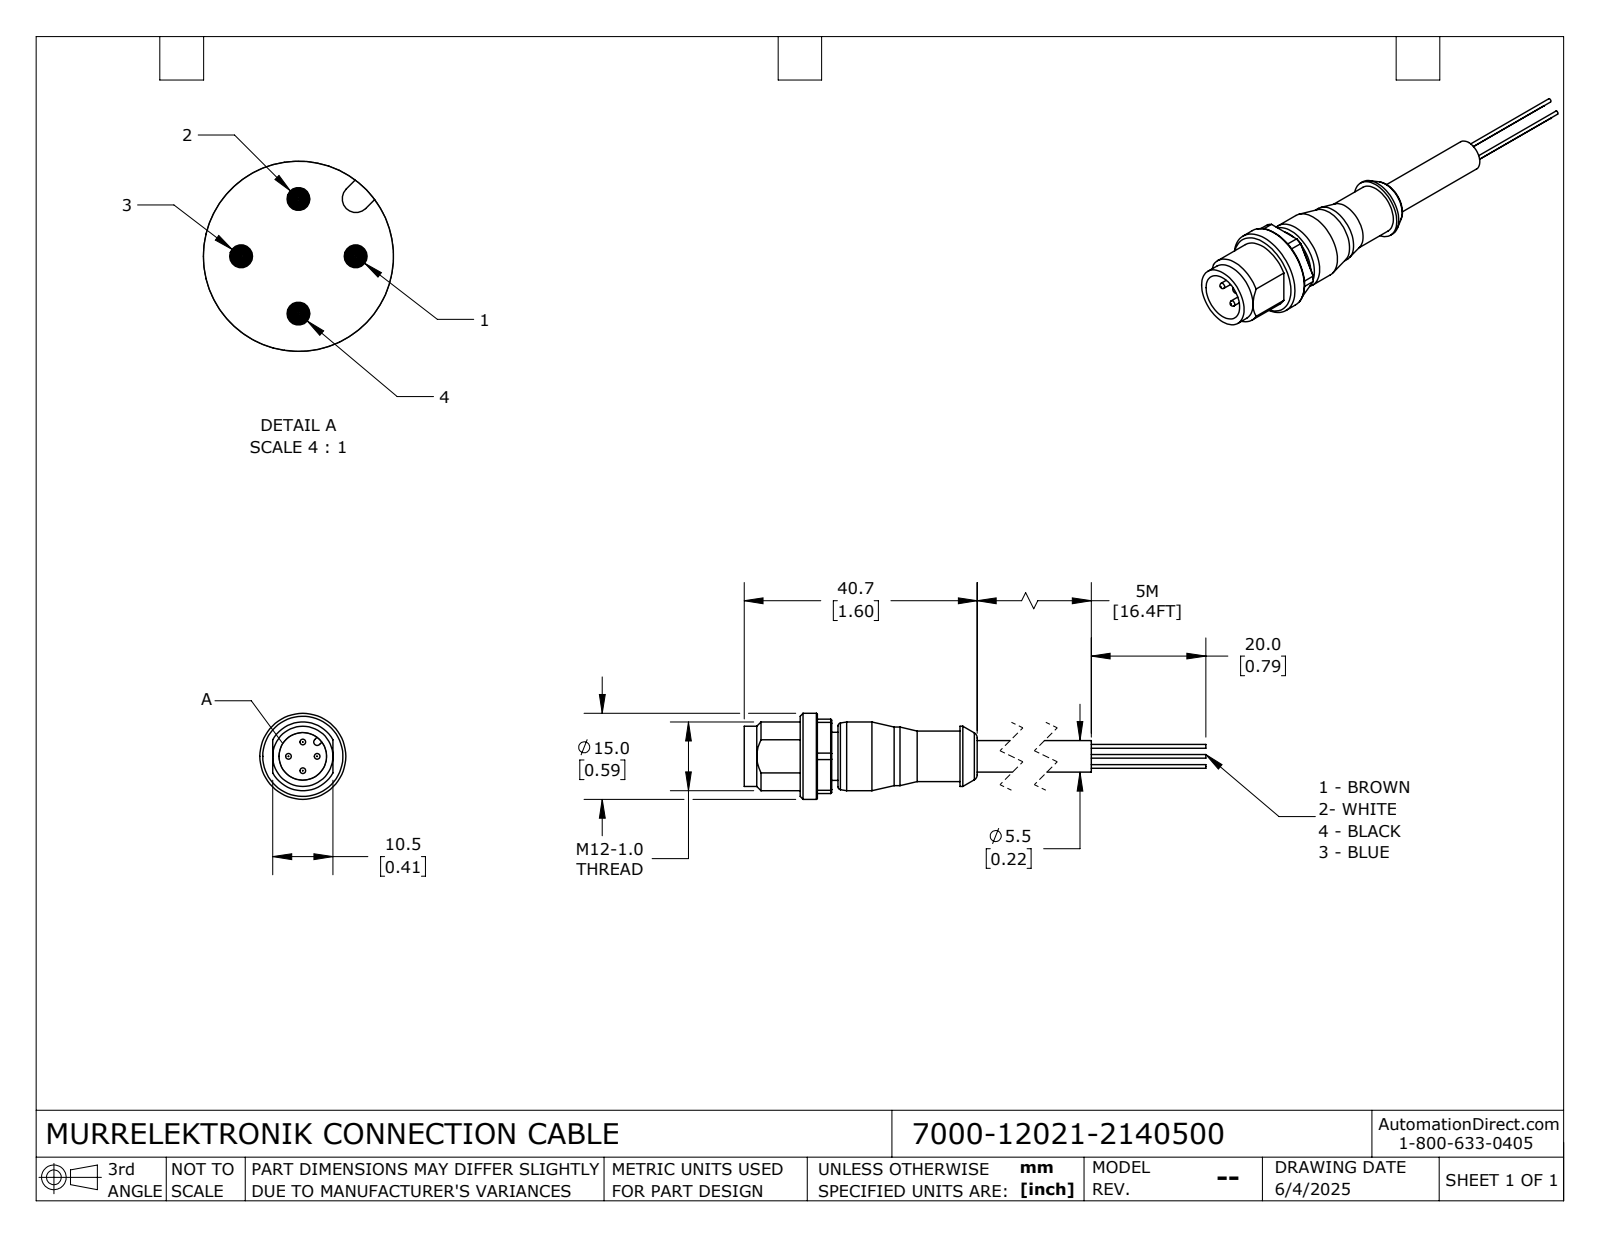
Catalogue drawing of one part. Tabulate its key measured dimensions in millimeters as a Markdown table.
| quantity | value |
| --- | --- |
| part name | 7000-12021-2140500 |
| STEP written by | SolidWorks 2024 (CONFIG_CONTROL_DESIGN) |
| units | millimeters |
| bodies | 1 solid, 110 faces (34 planar, 43 cylindrical, 33 other) |
| overall size | 80.7 × 15 × 15 |
| volume | 3 989 mm³ |
| surface area | 2 637 mm² |
| round holes (diameter × count) | 8.3 × 1 |
| round bosses / shafts (diameter × count) | 1 × 4, 0.64 × 4, 15 × 1, 12 × 1, 10.5 × 1, 10.2 × 1, 8.8 × 1, 8.4 × 1 |
| partial cylindrical surfaces (radius × count) | 0.6 × 1, 7.2 × 1 |
| main face-to-face distances | 6.4, 0.9, 5.5, 13, 10.5, 27.9, 7.5, 6.6, 1.1, 8.9 |
